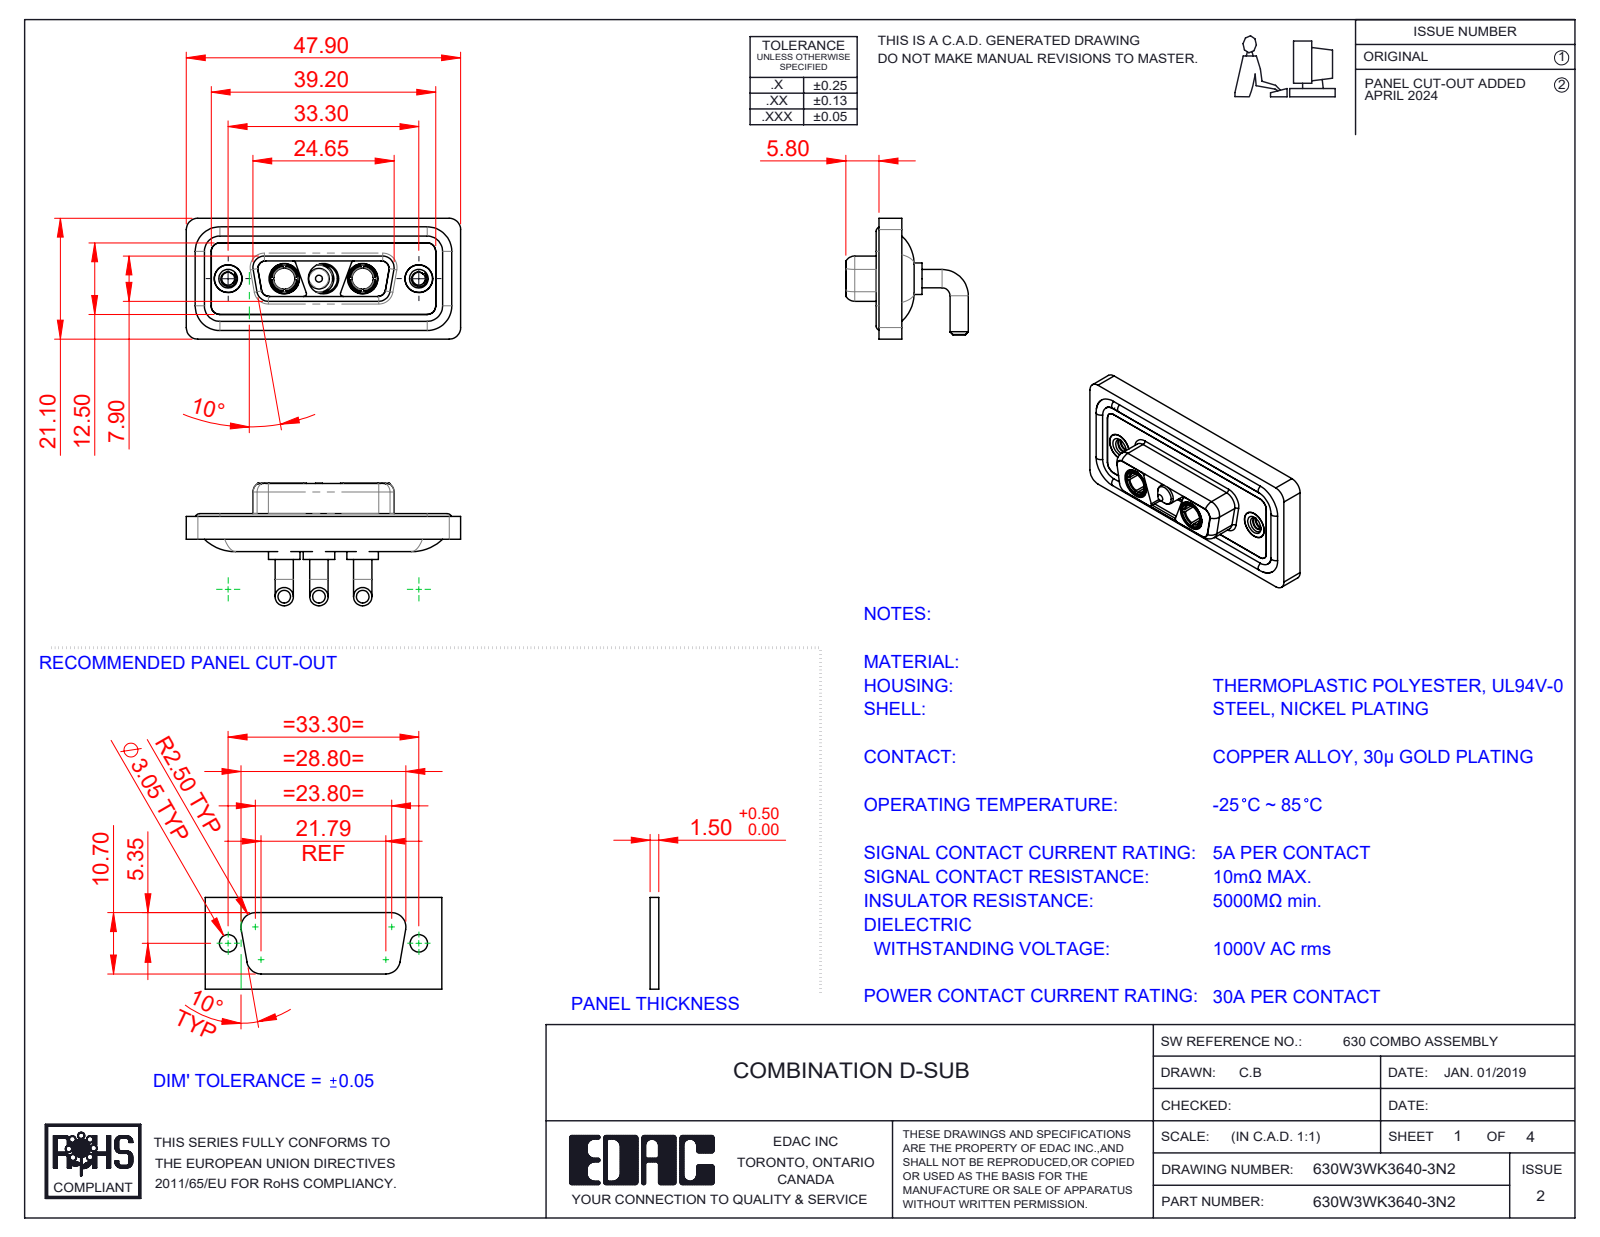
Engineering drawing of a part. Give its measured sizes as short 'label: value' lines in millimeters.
name: 630Combo Threaded Rivet_2; Power Socket_30A RA; Power Pin_30A RA; 630Combo Shell Front_15 Contacts (+4 more)
written by: SolidWorks 2023 (CONFIG_CONTROL_DESIGN)
unit: mm
bodies: 13 solids, 595 faces (178 planar, 264 cylindrical, 153 other)
size: 47.9 × 21.4 × 21.1
volume: 6 116 mm³; area: 9 793 mm²
holes: 5× ⌀4.85, 3× ⌀5.3, 2× ⌀2.26, 2× ⌀3.7, 2× ⌀4, 2× ⌀4.05, 2× ⌀5
bosses: 6× ⌀3.2, 4× ⌀1.6, 3× ⌀5.5, 3× ⌀5.2, 3× ⌀4.75, 3× ⌀3.75, 2× ⌀4.96, 2× ⌀4.95
rounds: 20× R2, 18× R1.5, 12× R1.35, 8× R0.5, 8× R1.6, 4× R0.25, 4× R0.6, 4× R0.65
face distances: 0.4, 1.8, 1.1, 1.6, 2.9, 2.5, 3.1, 3.7, 4.1, 1.5
hole spacings: 6.85, 9.8, 16.65, 23.5, 13.7, 33.3
